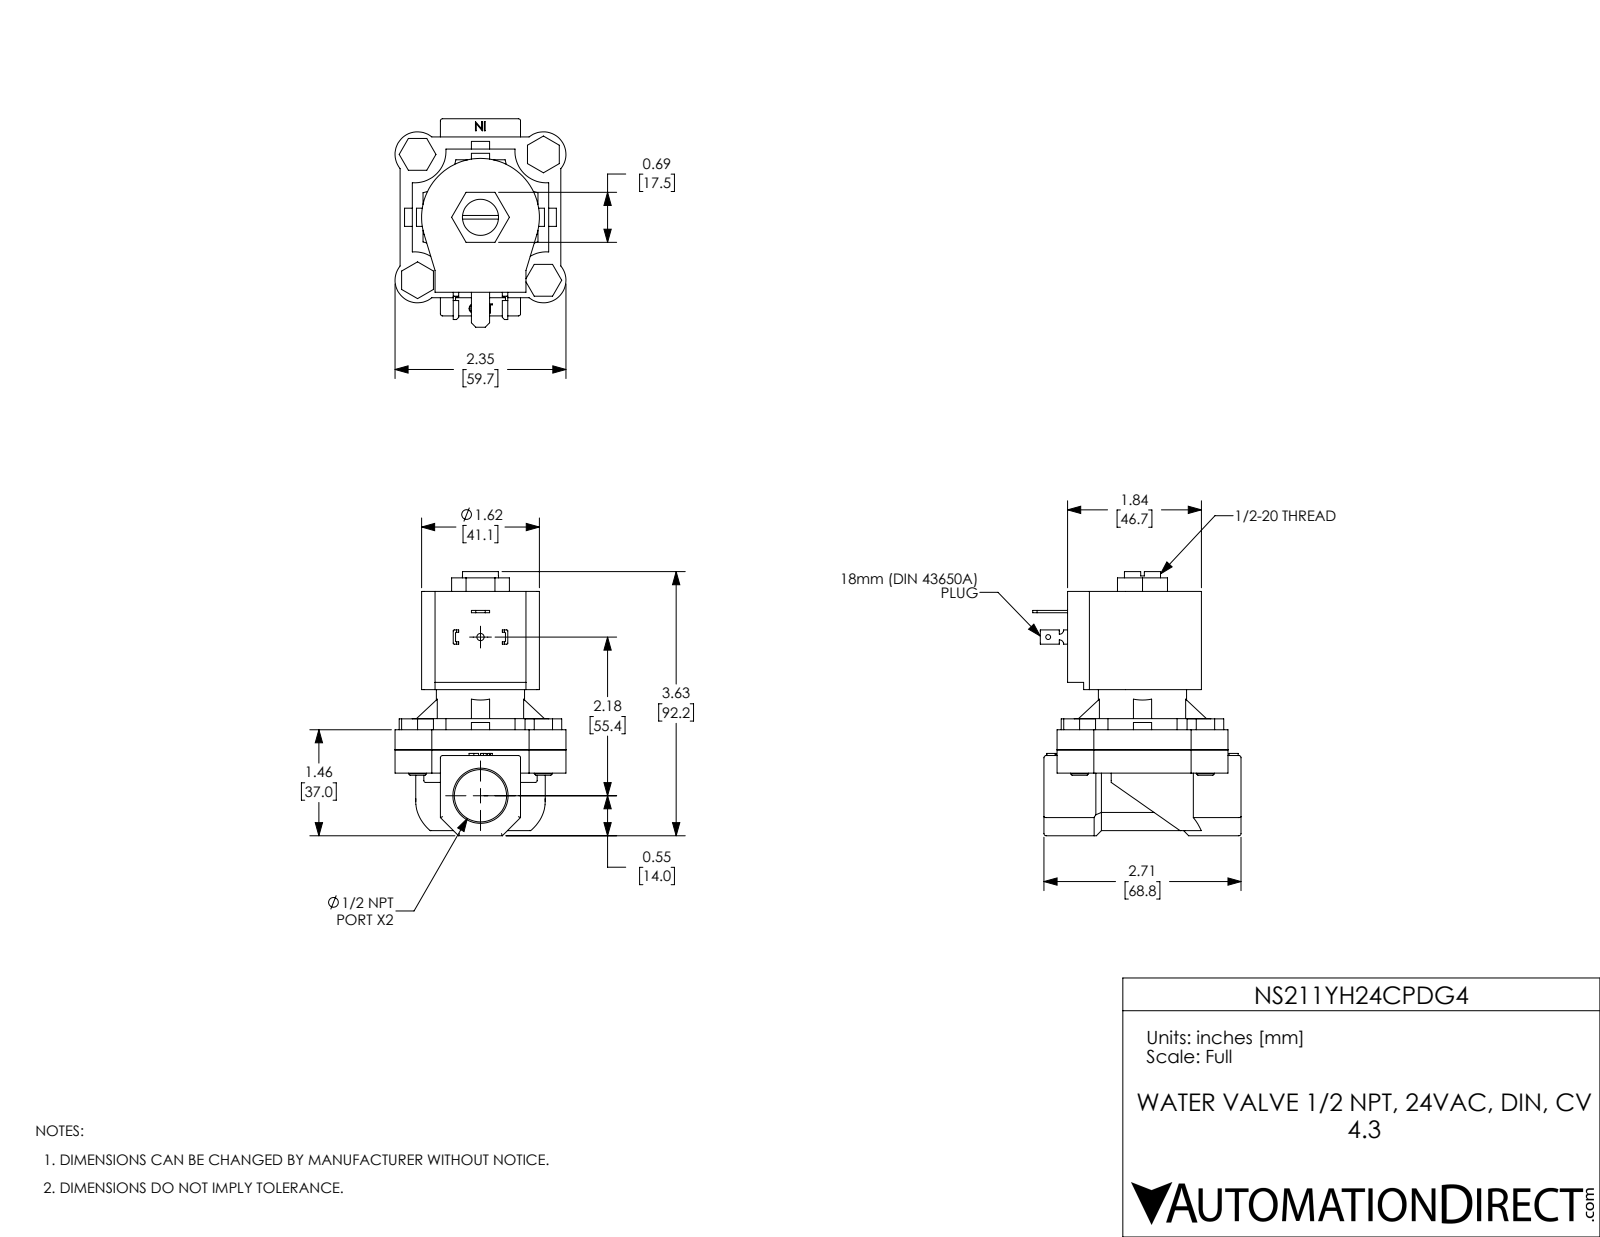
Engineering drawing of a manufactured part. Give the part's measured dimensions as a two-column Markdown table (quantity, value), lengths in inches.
| quantity | value |
| --- | --- |
| part name | NS211YH24CPDG4 |
| STEP written by | SolidWorks 2024 (CONFIG_CONTROL_DESIGN) |
| units | inches |
| bodies | 11 solids, 385 faces (239 planar, 113 cylindrical, 33 other) |
| overall size | 3.63 × 2.865 × 2.35 |
| volume | 9.473 in³ |
| surface area | 65.14 in² |
| round holes (diameter × count) | 0.25 × 4, 0.067 × 1, 0.1 × 1, 0.496 × 1, 0.512 × 1, 0.719 × 1, 1.155 × 1 |
| round bosses / shafts (diameter × count) | 0.248 × 4, 1.213 × 1 |
| partial cylindrical surfaces (radius × count) | 0.03 × 15, 0.015 × 8, 0.31 × 4, 0.432 × 4, 0.579 × 4, 0.06 × 2, 0.81 × 1, 0.89 × 1 |
| main face-to-face distances | 0.276, 2.177, 1.901, 0.32, 0.596, 2.497, 0.554, 1.656, 0.25, 1.147 |
| hole center spacings | 1.223, 1.73, 2.446, 2.181 |
